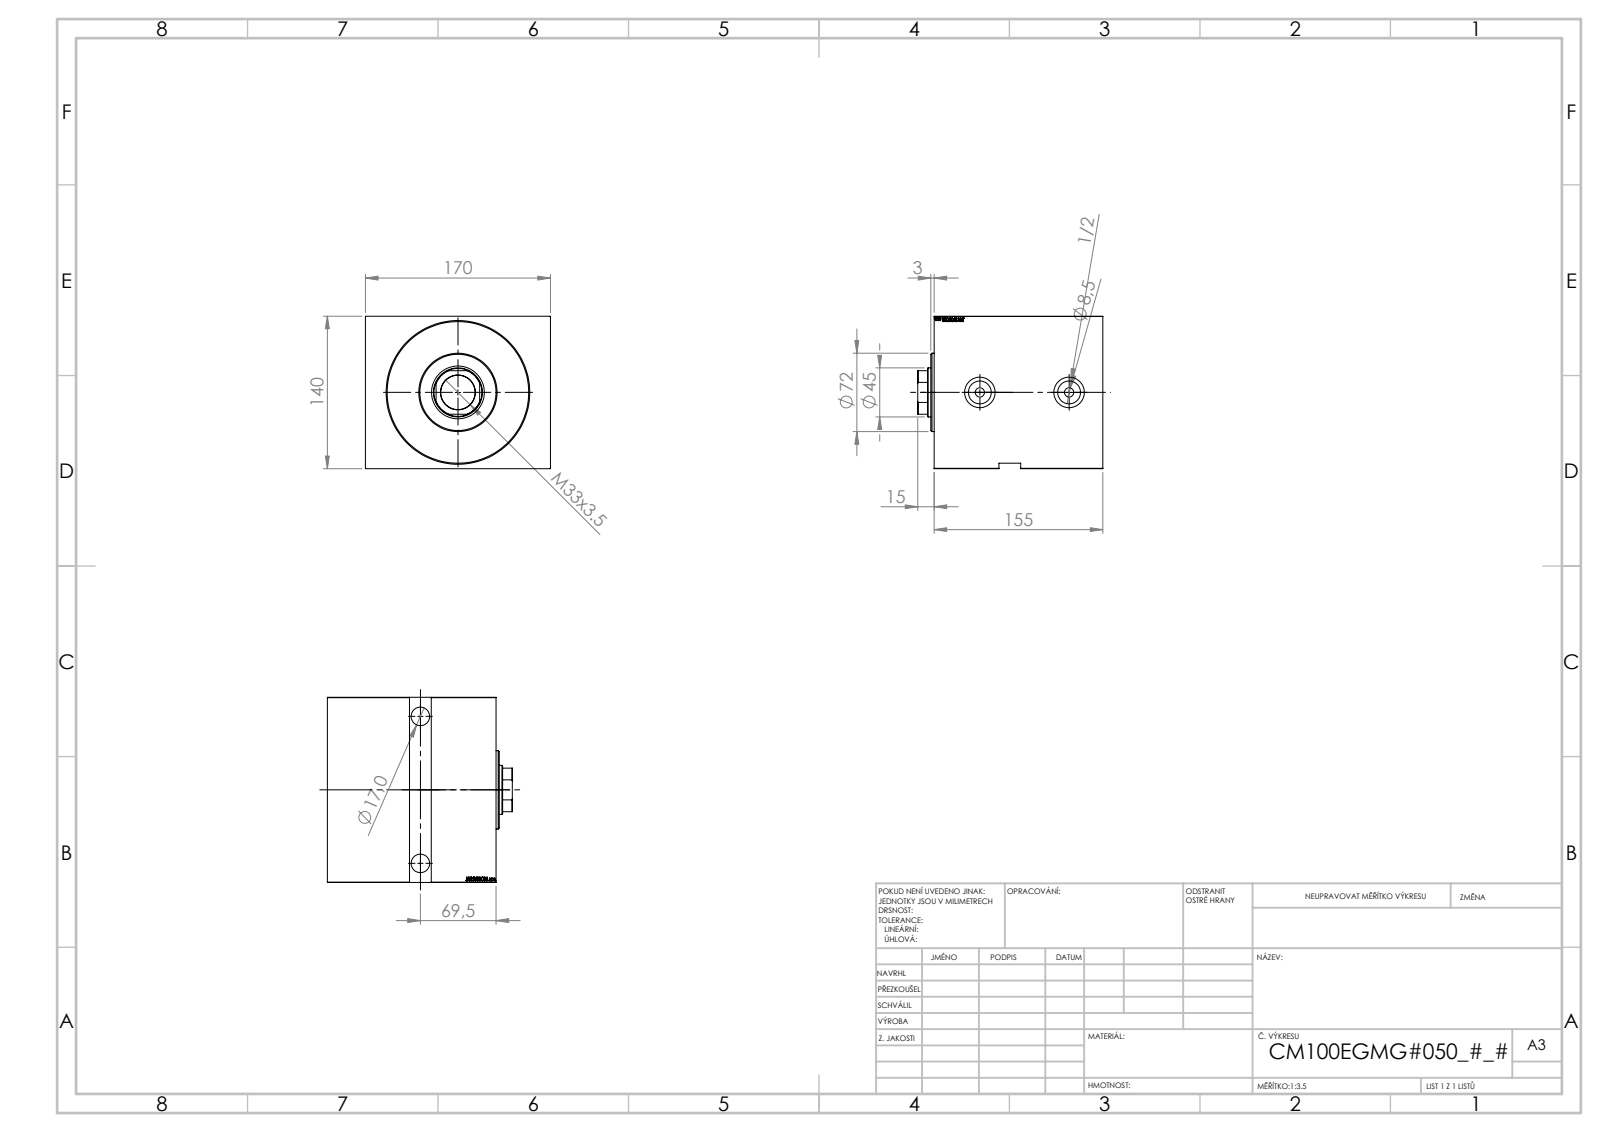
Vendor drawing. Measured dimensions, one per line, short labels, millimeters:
name: V450CM_VC_B; V450CM_E_Body; V450CM_E_VCP
written by: SolidWorks 2019 (CONFIG_CONTROL_DESIGN)
unit: mm
bodies: 3 solids, 851 faces (411 planar, 46 cylindrical, 394 other)
size: 170 × 170 × 140
volume: 3 099 000 mm³; area: 282 129 mm²
holes: 2× ⌀8.5, 2× ⌀17, 2× ⌀20.96, 2× ⌀25, 2× ⌀28, 1× ⌀31.5, 1× ⌀45, 1× ⌀48.5, 1× ⌀100, 1× ⌀102, 1× ⌀130
bosses: 1× ⌀72
rounds: 1× R22
face distances: 140, 170, 155, 26, 129, 5, 150, 124, 138.4, 112.4
hole spacings: 82, 135
